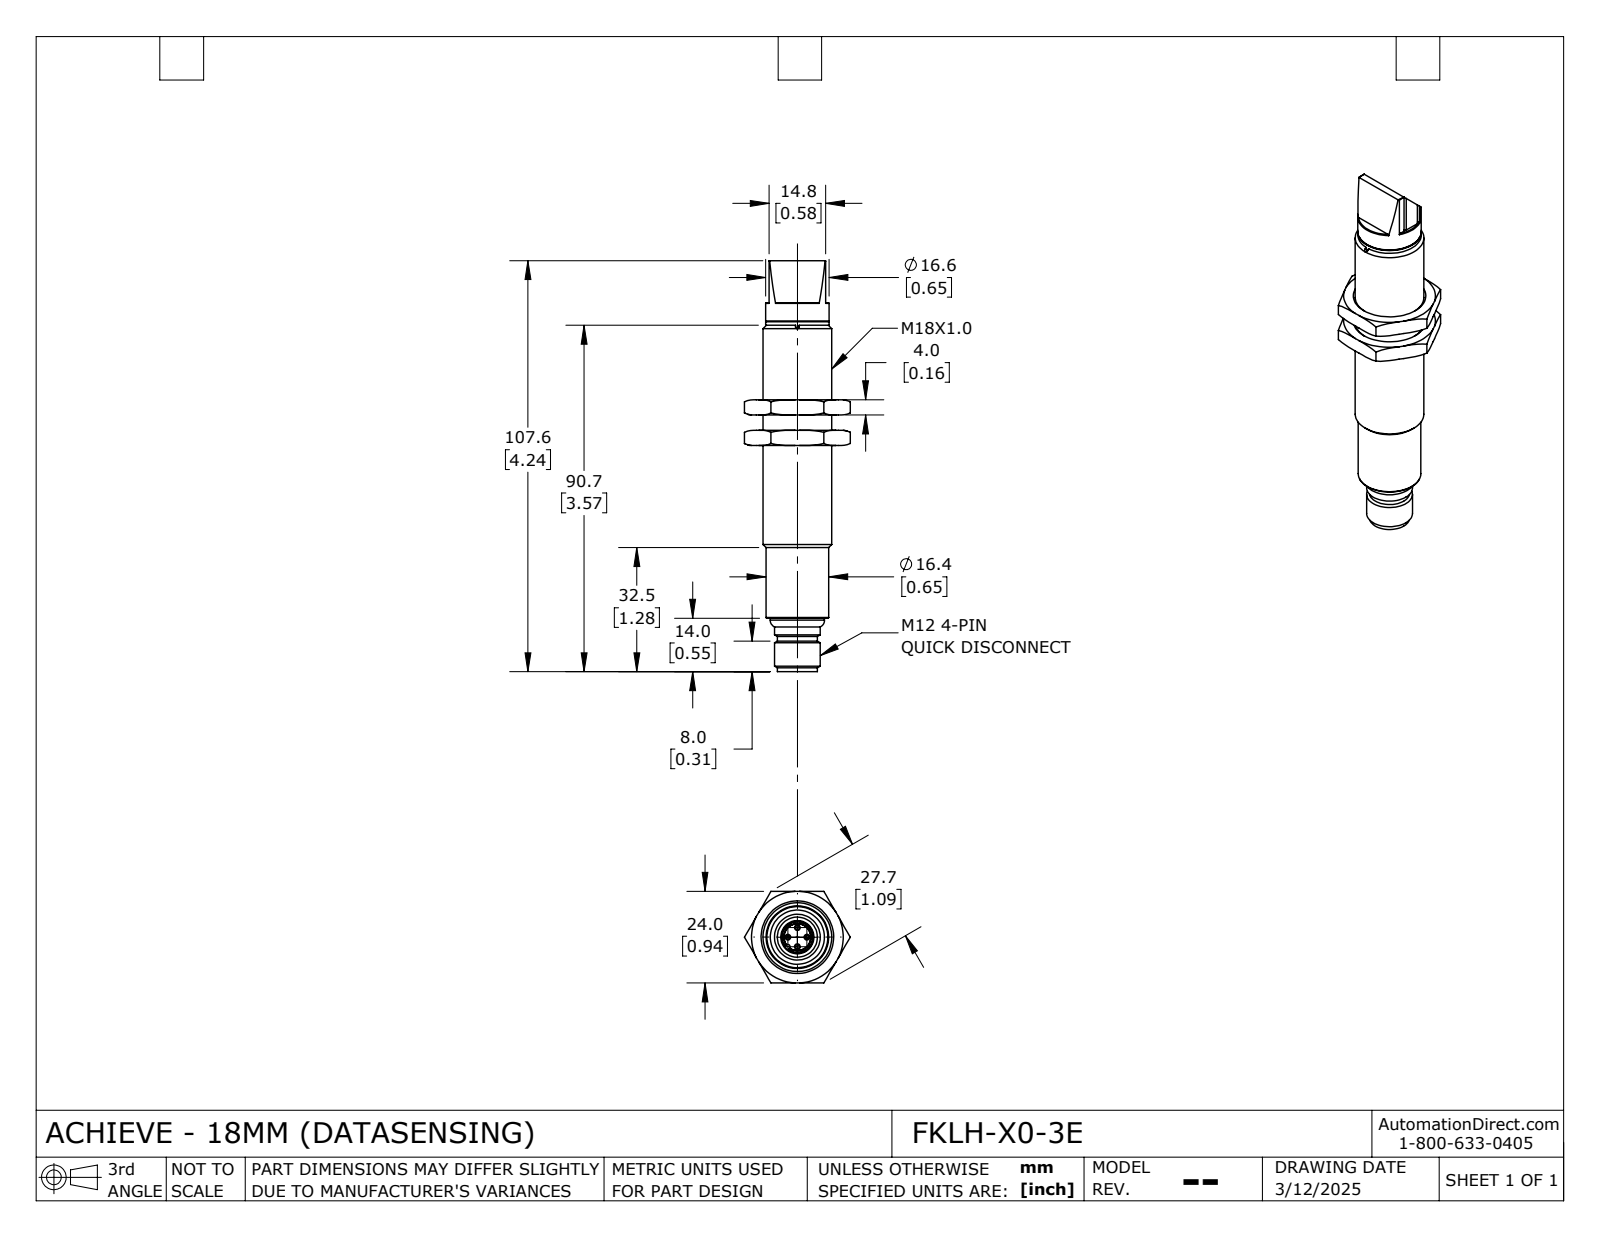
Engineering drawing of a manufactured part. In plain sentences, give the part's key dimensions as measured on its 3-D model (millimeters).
The part is named "FKLH-X0-3E_Default". Its 3-D file was written by "SolidWorks 2024 (CONFIG_CONTROL_DESIGN)". It is 3 solids with 138 faces: 62 planar, 25 cylindrical and 51 other. Overall it measures 107.6 by 27.7 by 24 millimeters. Its volume is 24 170 cubic millimeters and its surface area 8 974 square millimeters. Round holes: 1 of diameter 7.1, 1 of diameter 8.3, 1 of diameter 14.8, 1 of diameter 18. Round bosses or shafts: 4 of diameter 1, 1 of diameter 16.6, 1 of diameter 16.4, 1 of diameter 14.2, 1 of diameter 12, 1 of diameter 10.5, 1 of diameter 7. Partial cylindrical surfaces (rounded edges, fillets, slot ends): 2 of radius 0.1, 2 of radius 0.5, 1 of radius 0.6, 1 of radius 7.5. The main face-to-face distances are 4, 8, 24, 12, 31.9, 32.1, 23.9, 24.1, 35.9, 36.1.
